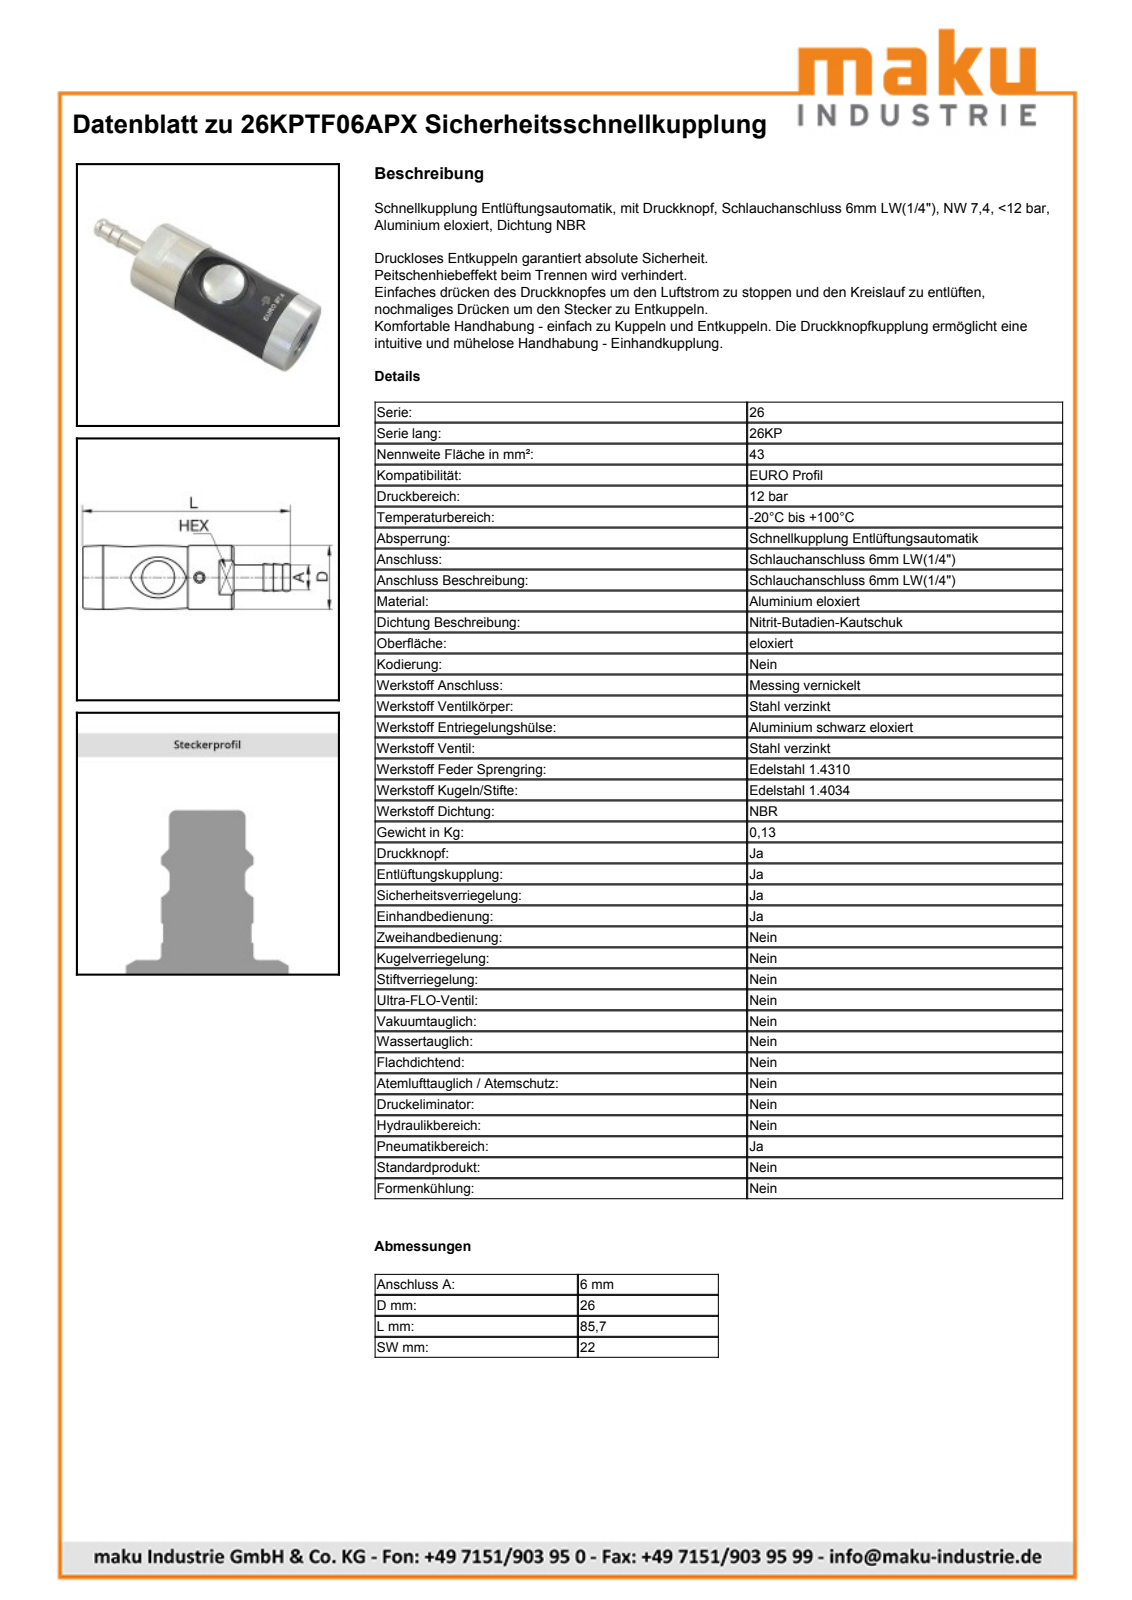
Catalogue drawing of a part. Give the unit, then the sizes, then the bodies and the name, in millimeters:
Units: millimetres
Overall size (bounding box): 85.7 × 26 × 26
Round holes (diameter × count): ⌀12.4 ×2, ⌀3.5 ×1, ⌀6 ×1, ⌀6.5 ×1, ⌀7 ×1, ⌀9.65 ×1, ⌀10.1 ×1, ⌀10.6 ×1, ⌀12.1 ×1, ⌀12.25 ×1, ⌀12.8 ×1, ⌀13.6 ×1
Round bosses / shafts (diameter × count): ⌀26 ×1, ⌀22 ×1, ⌀21.33 ×1, ⌀18.1 ×1, ⌀17.8 ×1, ⌀16.72 ×1, ⌀16.5 ×1, ⌀15.8 ×1
Partial cylindrical surfaces — rounded edges, fillets, slot ends (radius × count): R6.2 ×2, R4.4 ×1
Main face-to-face distances: 19, 43.4, 8.4, 62.4, 54, 35, 1.3, 22, 7.7, 21.6
Hole centre spacings: 0.6, 0.7, 1.3, 17.05
Volume: 38 832 mm³ · Surface area: 24 951 mm²
Bodies: 39 solids, 255 faces (72 planar, 83 cylindrical, 100 other)
Part name (STEP PRODUCT): 26KPTF06APX
STEP written by: Autodesk Inventor 2019 (AUTOMOTIVE_DESIGN)
